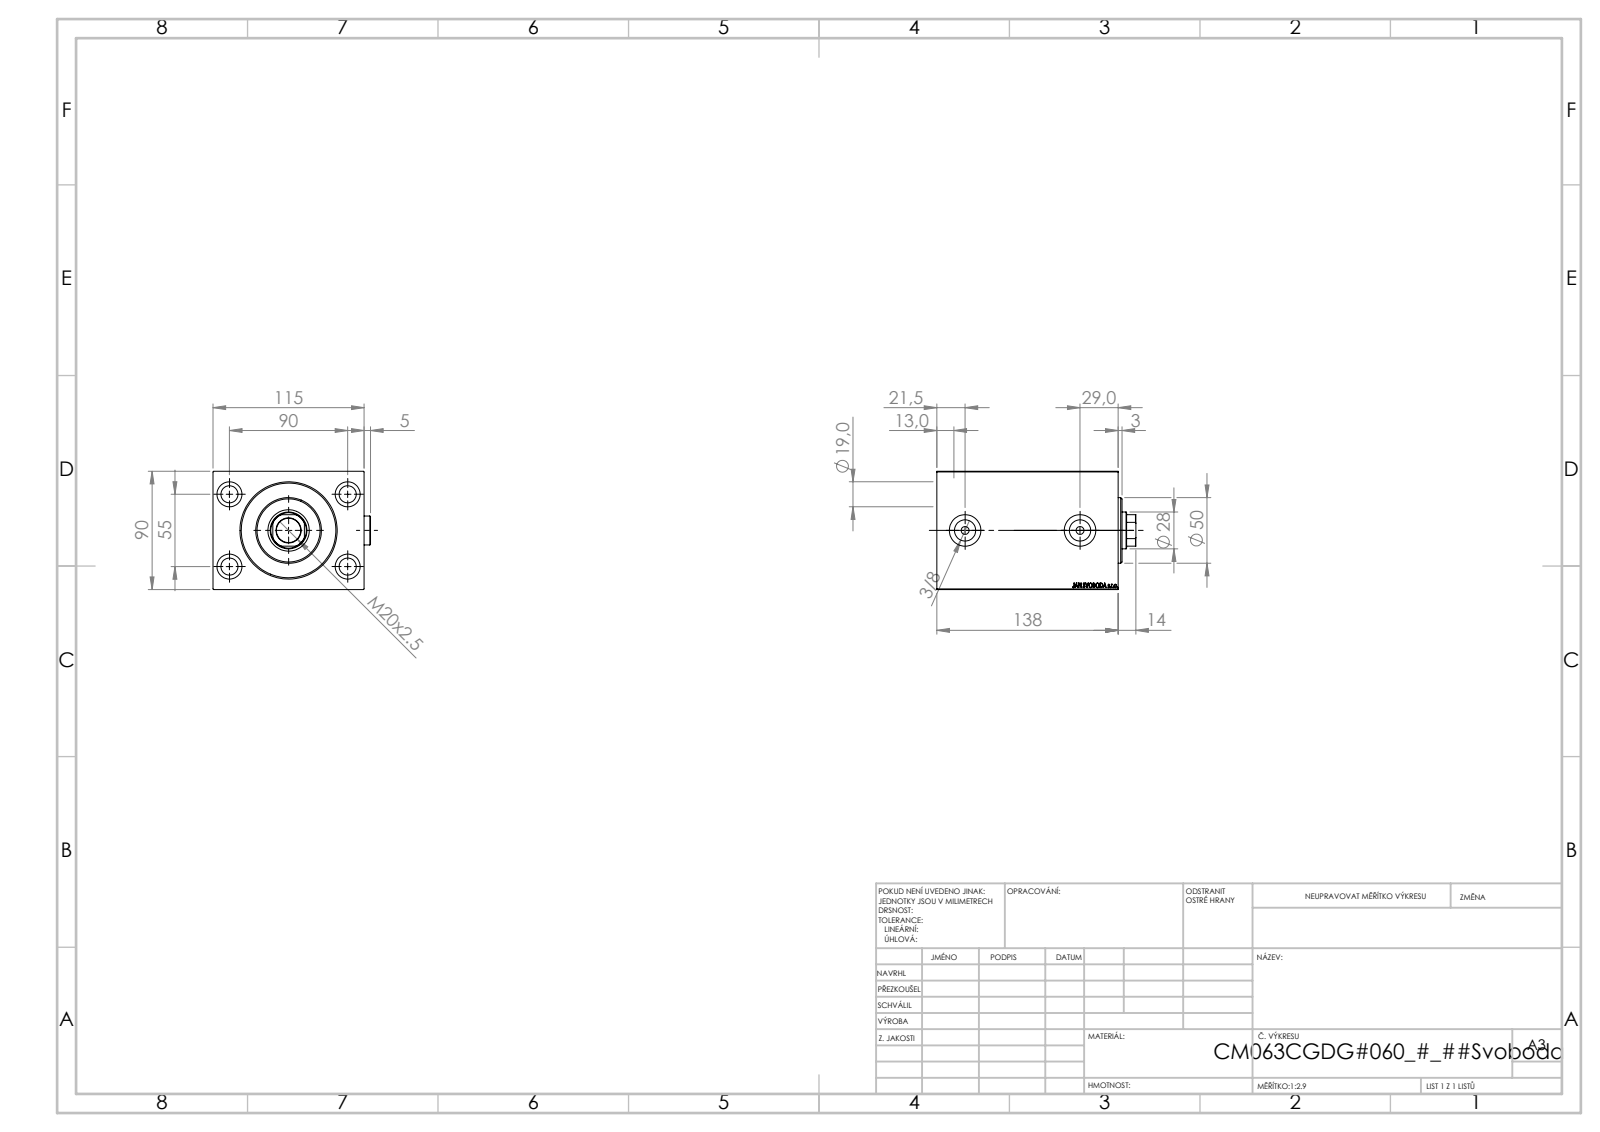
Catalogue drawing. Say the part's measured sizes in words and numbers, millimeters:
The part is named "V450CM_C_VCP; V450CM_VC_B; V450CM_C_Body; Zatka_OIL_PORT". Its 3-D file was written by "SolidWorks 2019 (CONFIG_CONTROL_DESIGN)". It is 5 solids with 919 faces: 443 planar, 78 cylindrical and 398 other. Overall it measures 151.5 by 119.9 by 90 millimeters. Its volume is 1 184 000 cubic millimeters and its surface area 166 593 square millimeters. Round holes: 4 of diameter 13, 4 of diameter 19, 2 of diameter 6, 2 of diameter 16.17, 2 of diameter 24, 1 of diameter 18.5, 1 of diameter 28, 1 of diameter 31.5, 1 of diameter 63, 1 of diameter 65, 1 of diameter 72. Round bosses or shafts: 2 of diameter 22, 1 of diameter 50. Partial cylindrical surfaces (rounded edges, fillets, slot ends): 1 of radius 13.5. The main face-to-face distances are 90, 115, 138, 17.5, 120.5, 13.5, 107, 124.5, 64.5, 73.5. The hole center spacings are 52.74, 55, 90, 105.48, 87.5.
